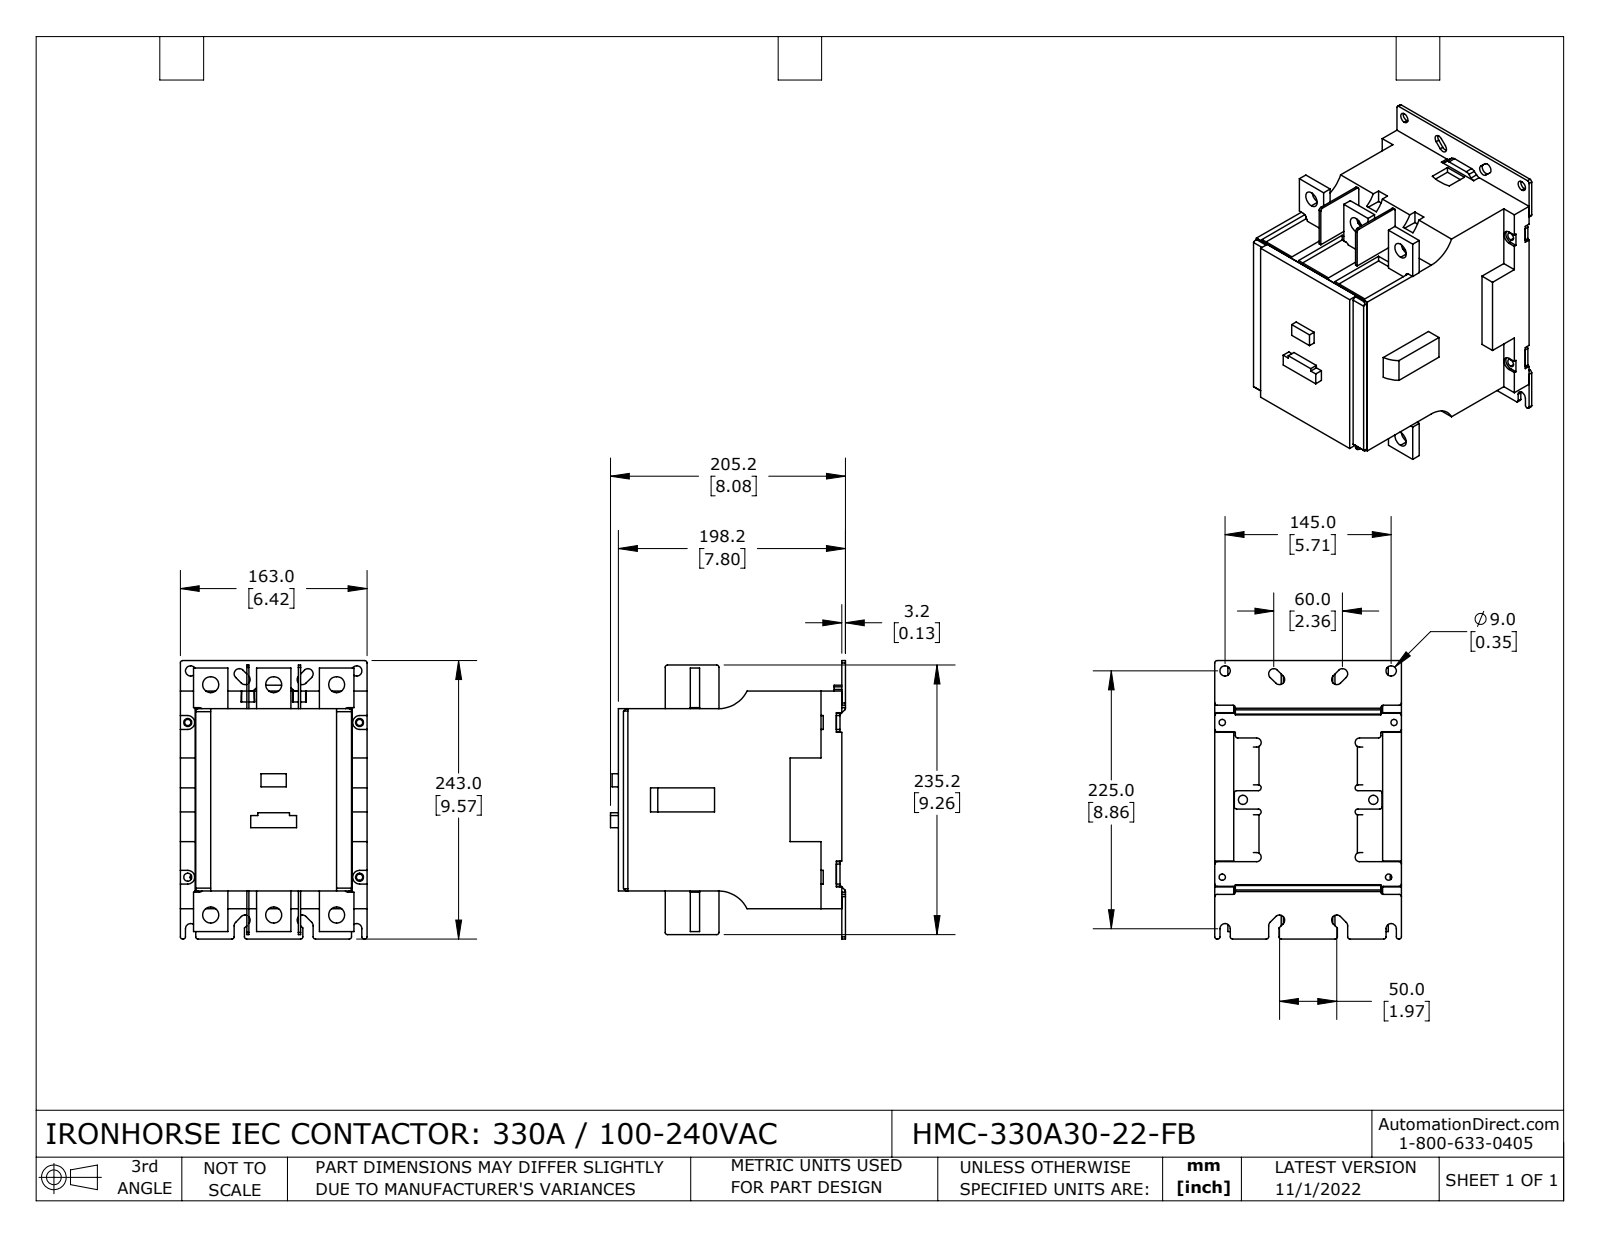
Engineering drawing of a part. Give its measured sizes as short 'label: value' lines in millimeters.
name: HMC-330A30-22-FB
written by: SolidWorks 2021 (CONFIG_CONTROL_DESIGN)
unit: mm
bodies: 9 solids, 491 faces (308 planar, 145 cylindrical, 38 other)
size: 243 × 205.2 × 163
volume: 4 787 000 mm³; area: 356 000 mm²
holes: 6× ⌀14, 4× ⌀7, 3× ⌀5.5, 2× ⌀8, 2× ⌀9
rounds: 52× R2, 10× R4.5, 4× R1, 4× R2.5, 4× R4, 4× R5, 4× R5.2, 4× R6
face distances: 182, 3.2, 4.7, 137, 186.7, 1.5, 195, 190.3, 8.3, 185.2
hole spacings: 38.6, 55, 69.9, 81.9, 100.5, 115.5, 134.1, 148.2
